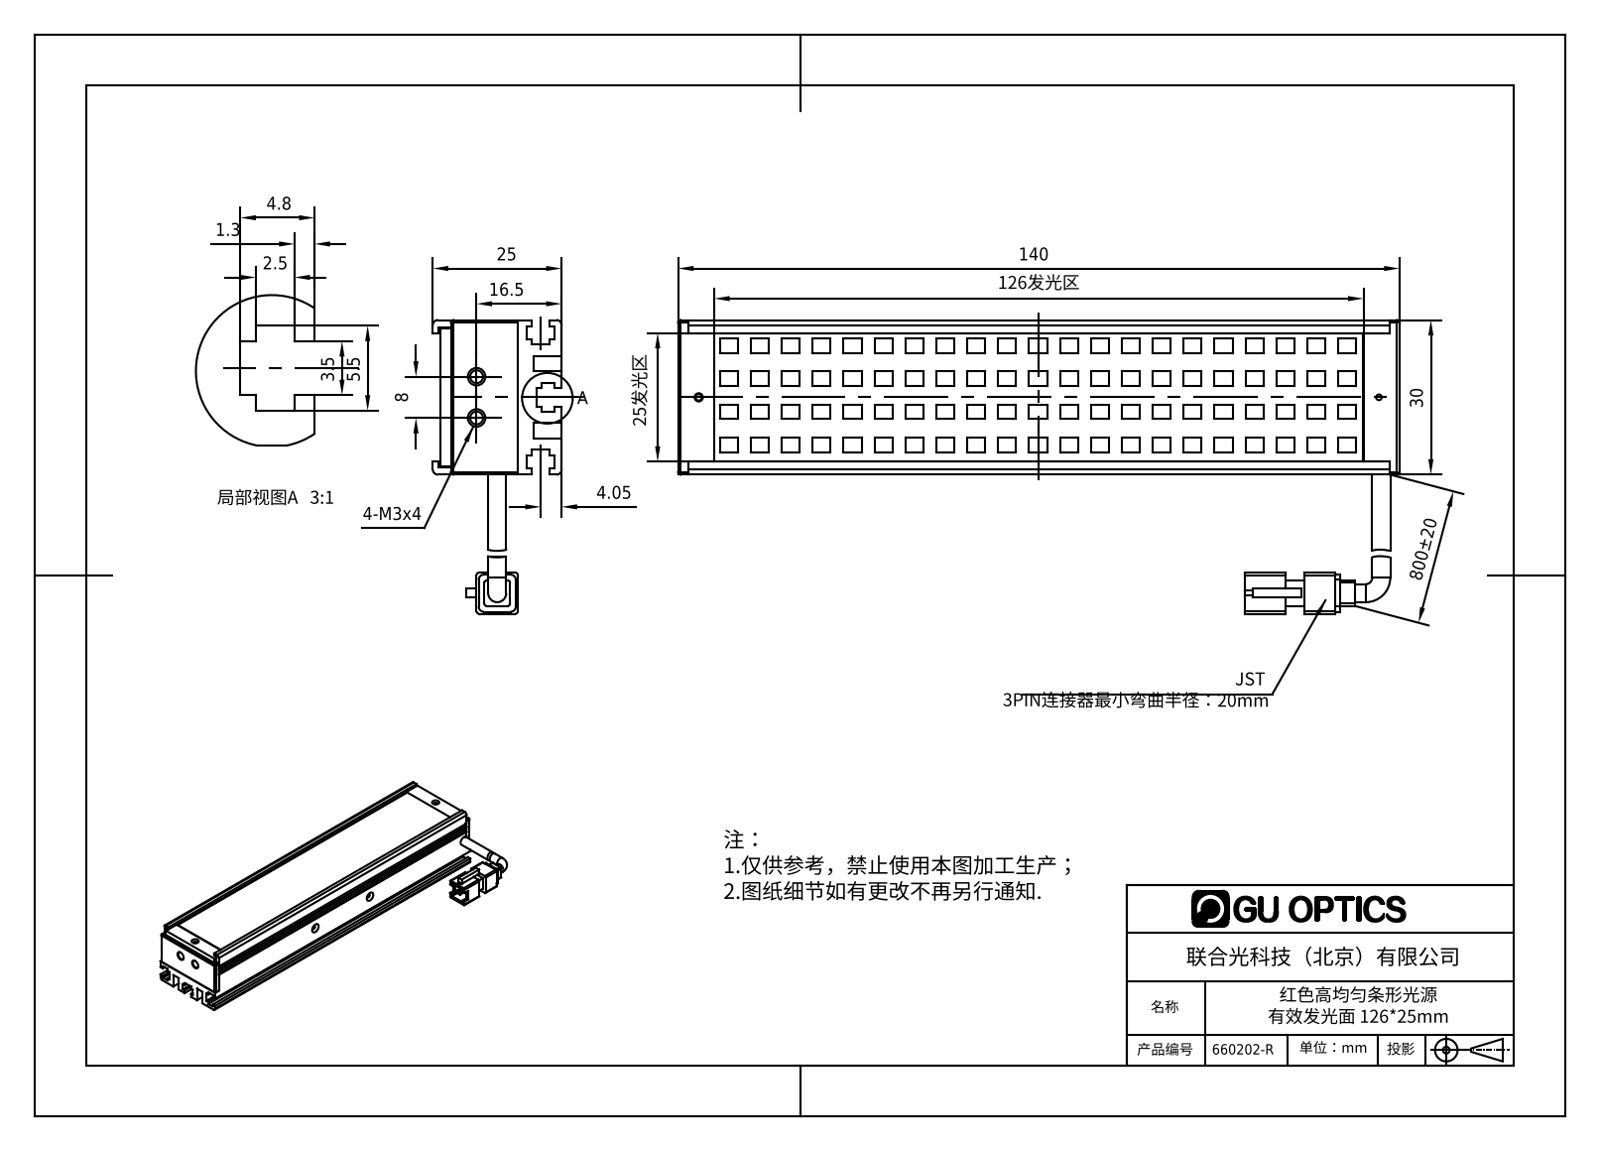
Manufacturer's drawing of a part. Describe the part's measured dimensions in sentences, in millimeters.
The part is named "660202-R". Its 3-D file was written by "SolidWorks 2016 (AUTOMOTIVE_DESIGN)". It is 6 solids with 864 faces: 678 planar, 83 cylindrical and 103 other. Overall it measures 140 by 57 by 25 millimeters. Its volume is 49 865 cubic millimeters and its surface area 50 427 square millimeters. Round holes: 5 of diameter 1.6, 2 of diameter 1.5, 2 of diameter 1.7, 2 of diameter 2.5, 2 of diameter 2.8, 2 of diameter 3, 1 of diameter 1.1, 1 of diameter 1.25, 1 of diameter 2. Round bosses or shafts: 2 of diameter 3.5. Partial cylindrical surfaces (rounded edges, fillets, slot ends): 12 of radius 1, 8 of radius 0.5, 1 of radius 1.65. The main face-to-face distances are 1, 13, 2, 2.5, 3, 9.5, 27.5, 4.5, 8.5, 21.5. The hole center spacings are 132, 7, 51, 51.43, 81, 81.27, 132.19, 8.
